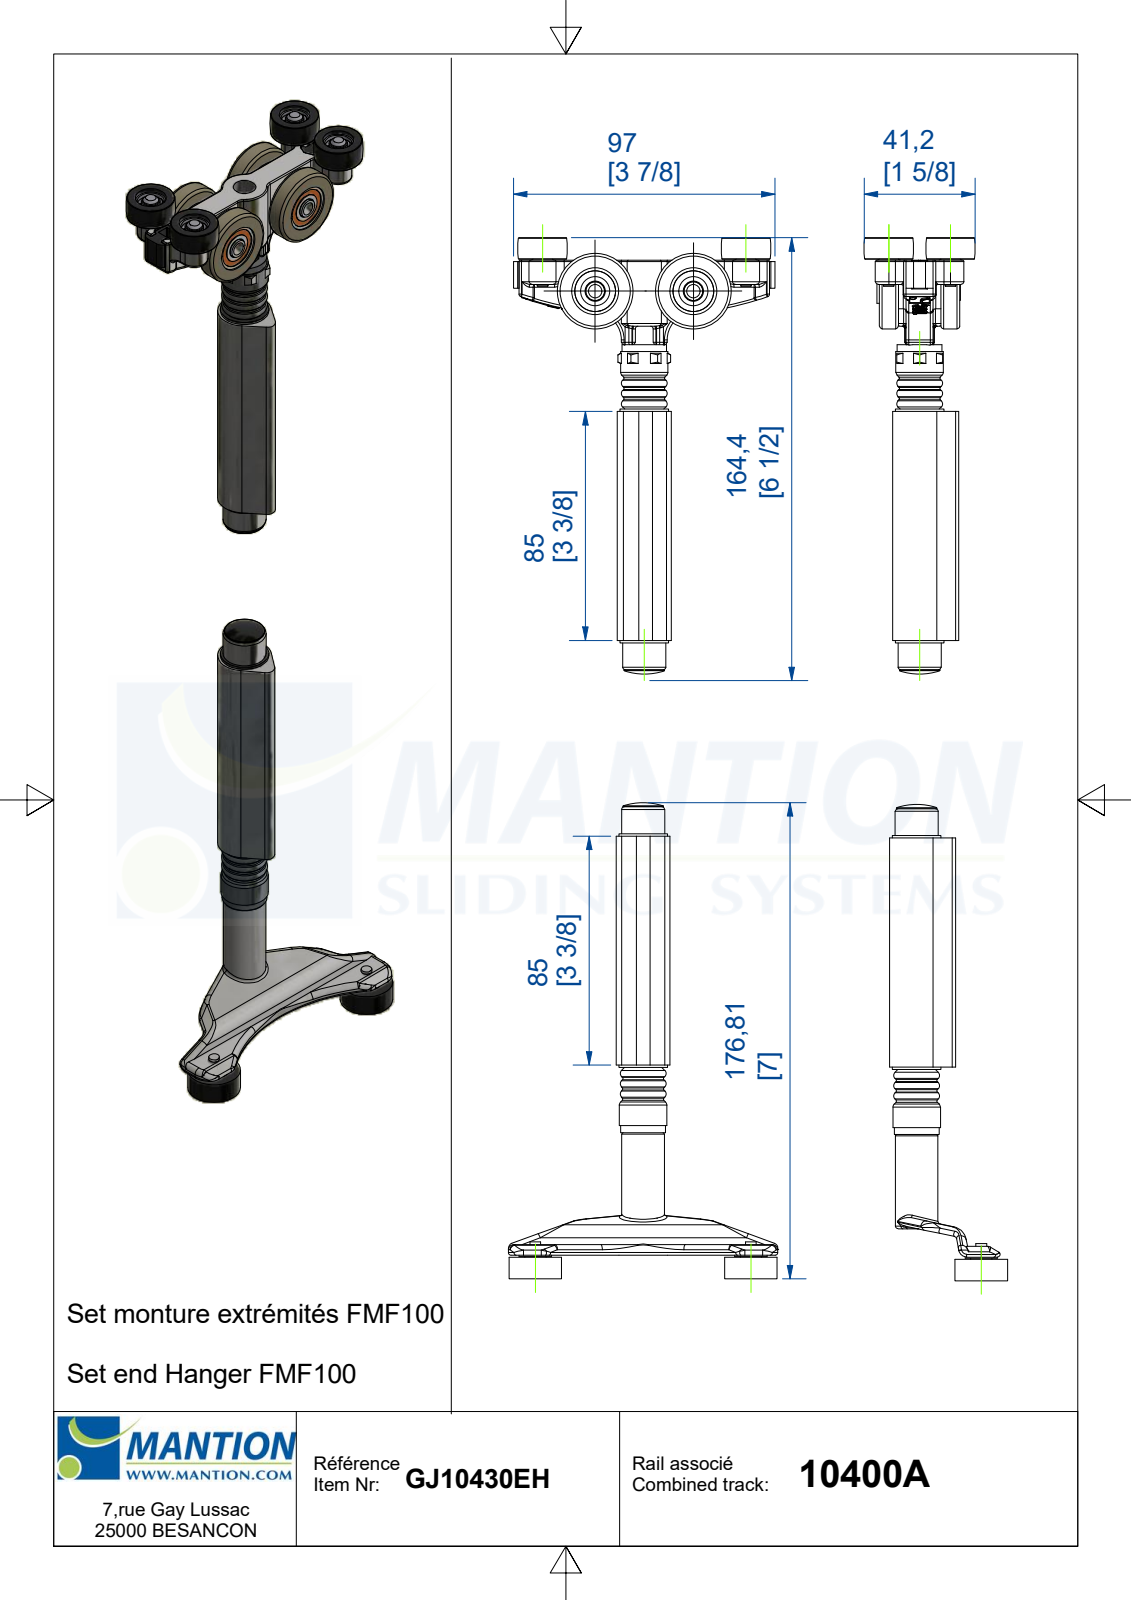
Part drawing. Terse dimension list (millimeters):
name: Ensemble3; GJ10430EH-Guide bas; 1107; 22837 (+8 more)
written by: Autodesk Inventor 2019 (AUTOMOTIVE_DESIGN)
unit: mm
bodies: 46 solids, 1527 faces (437 planar, 439 cylindrical, 651 other)
size: 343.44 × 100 × 54.43
volume: 133 654 mm³; area: 91 592 mm²
holes: 6× ⌀4, 4× ⌀10.12, 4× ⌀11.5, 4× ⌀13, 2× ⌀4.1, 2× ⌀4.8, 2× ⌀7, 2× ⌀7.05, 2× ⌀8.1, 2× ⌀15, 2× ⌀15.16, 2× ⌀17.5
bosses: 5× ⌀6, 4× ⌀6.88, 4× ⌀6.5, 3× ⌀13, 3× ⌀12, 2× ⌀28, 2× ⌀19.5, 2× ⌀15.14
rounds: 59× R1, 31× R0.2, 29× R0.5, 19× R3, 13× R2, 8× R0.25, 4× R3.3, 4× R3.5
face distances: 6.5, 7, 10, 0.5, 22.8, 22.81, 5, 333.94, 1.5, 6.51
hole spacings: 22.9, 39.44, 39.45, 46.65, 75.5, 12.68, 12.82, 35.44
